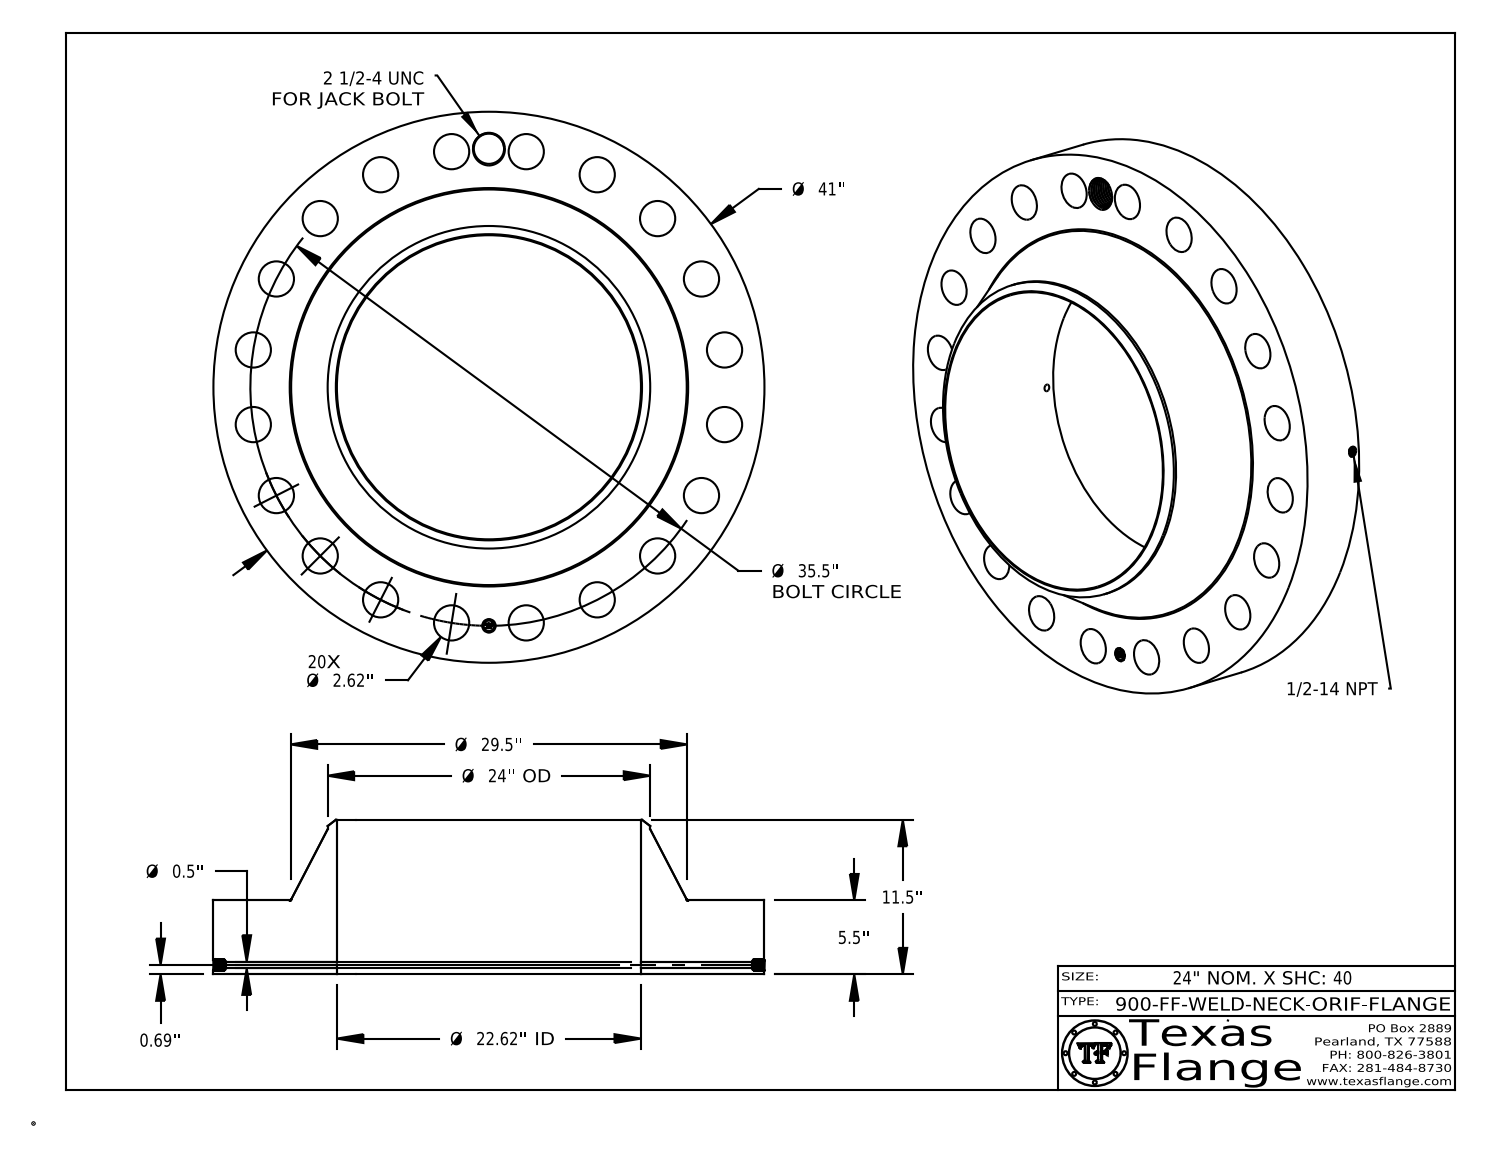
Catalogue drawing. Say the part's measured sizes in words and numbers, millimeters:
The part is named "900-FF-WELD-NECK". Its 3-D file was written by "CATIA V5 STEP AP214 (AUTOMOTIVE_DESIGN)". It is 1 solid with 832 faces: 368 planar, 130 cylindrical and 334 other. Overall it measures 1041.4 by 1041.4 by 292.1 millimeters. Its volume is 87 050 000 cubic millimeters and its surface area 2 859 000 square millimeters. Round holes: 20 of diameter 66.5, 1 of diameter 12.7, 1 of diameter 17.1, 1 of diameter 25.4, 1 of diameter 57.2, 1 of diameter 574.6. Round bosses or shafts: 8 of diameter 1.5, 1 of diameter 1041.4, 1 of diameter 609.6, 1 of diameter 20. The main face-to-face distances are 139.7, 292.1, 152.4, 139.3, 0.4, 152.8, 7.6, 7.4, 1.4, 6.3. The hole center spacings are 450.9, 278.6, 637.6, 729.5, 803.4, 890.6, 530, 857.6.
